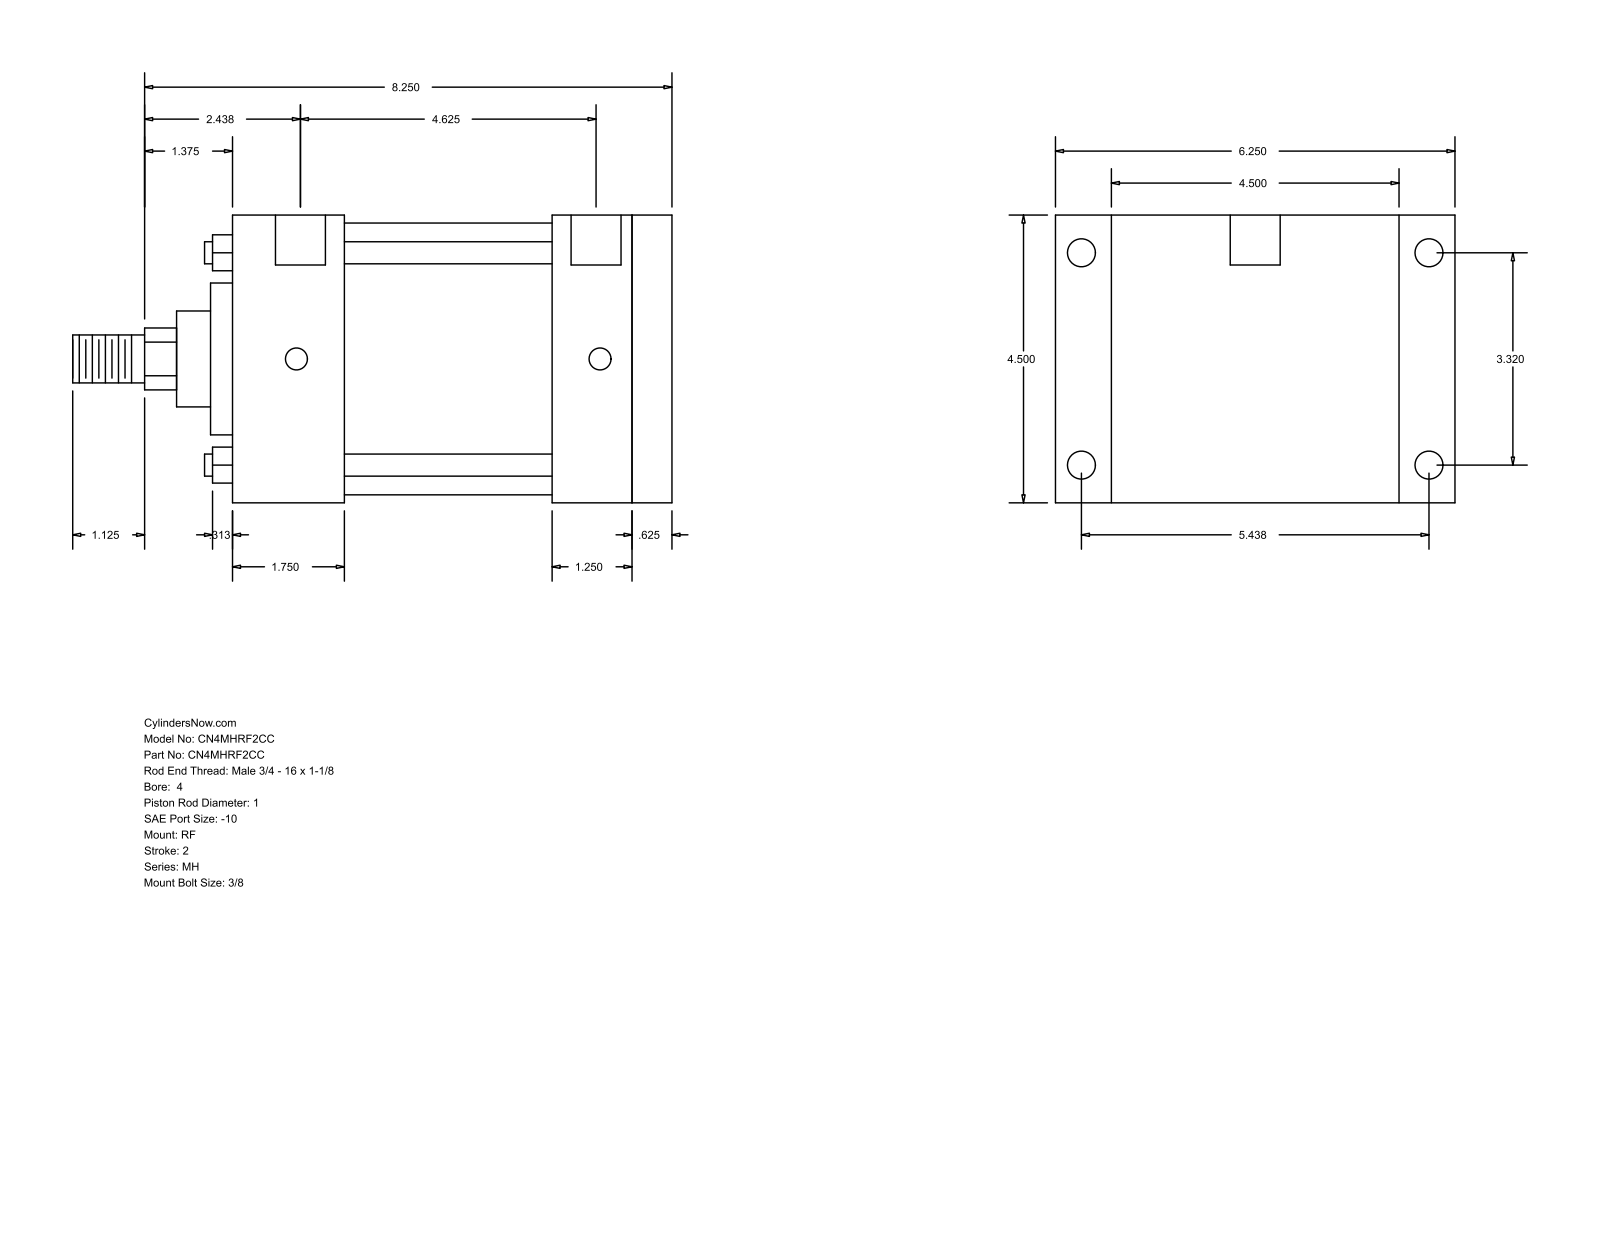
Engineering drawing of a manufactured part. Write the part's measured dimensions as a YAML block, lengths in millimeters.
part_name: "MH_RF__0400_1"
step_written_by: "GSSL Pune (CONFIG_CONTROL_DESIGN)"
units: millimeters
bodies: {solids: 0, faces: 94, planar: 65, cylindrical: 29, other: 0}
overall_size: [238.12, 158.75, 114.3]
round_holes:
  - {diameter: 8.73, count: 4}
  - {diameter: 11.13, count: 4}
  - {diameter: 19.84, count: 2}
round_bosses_or_shafts:
  - {diameter: 8.76, count: 4}
  - {diameter: 107.95, count: 1}
  - {diameter: 60.33, count: 1}
  - {diameter: 38.1, count: 1}
  - {diameter: 25.4, count: 1}
  - {diameter: 19.05, count: 1}
partial_cylinders:
  - {radius: 12.29, count: 1}
face_to_face_distances: [114.3, 174.63, 158.76, 15.87, 44.46, 130.17, 127.01, 82.55, 31.75, 47.62]
hole_center_spacings: [1.58, 84.32, 119.06, 120.64, 138.12, 161.82, 117.48]
